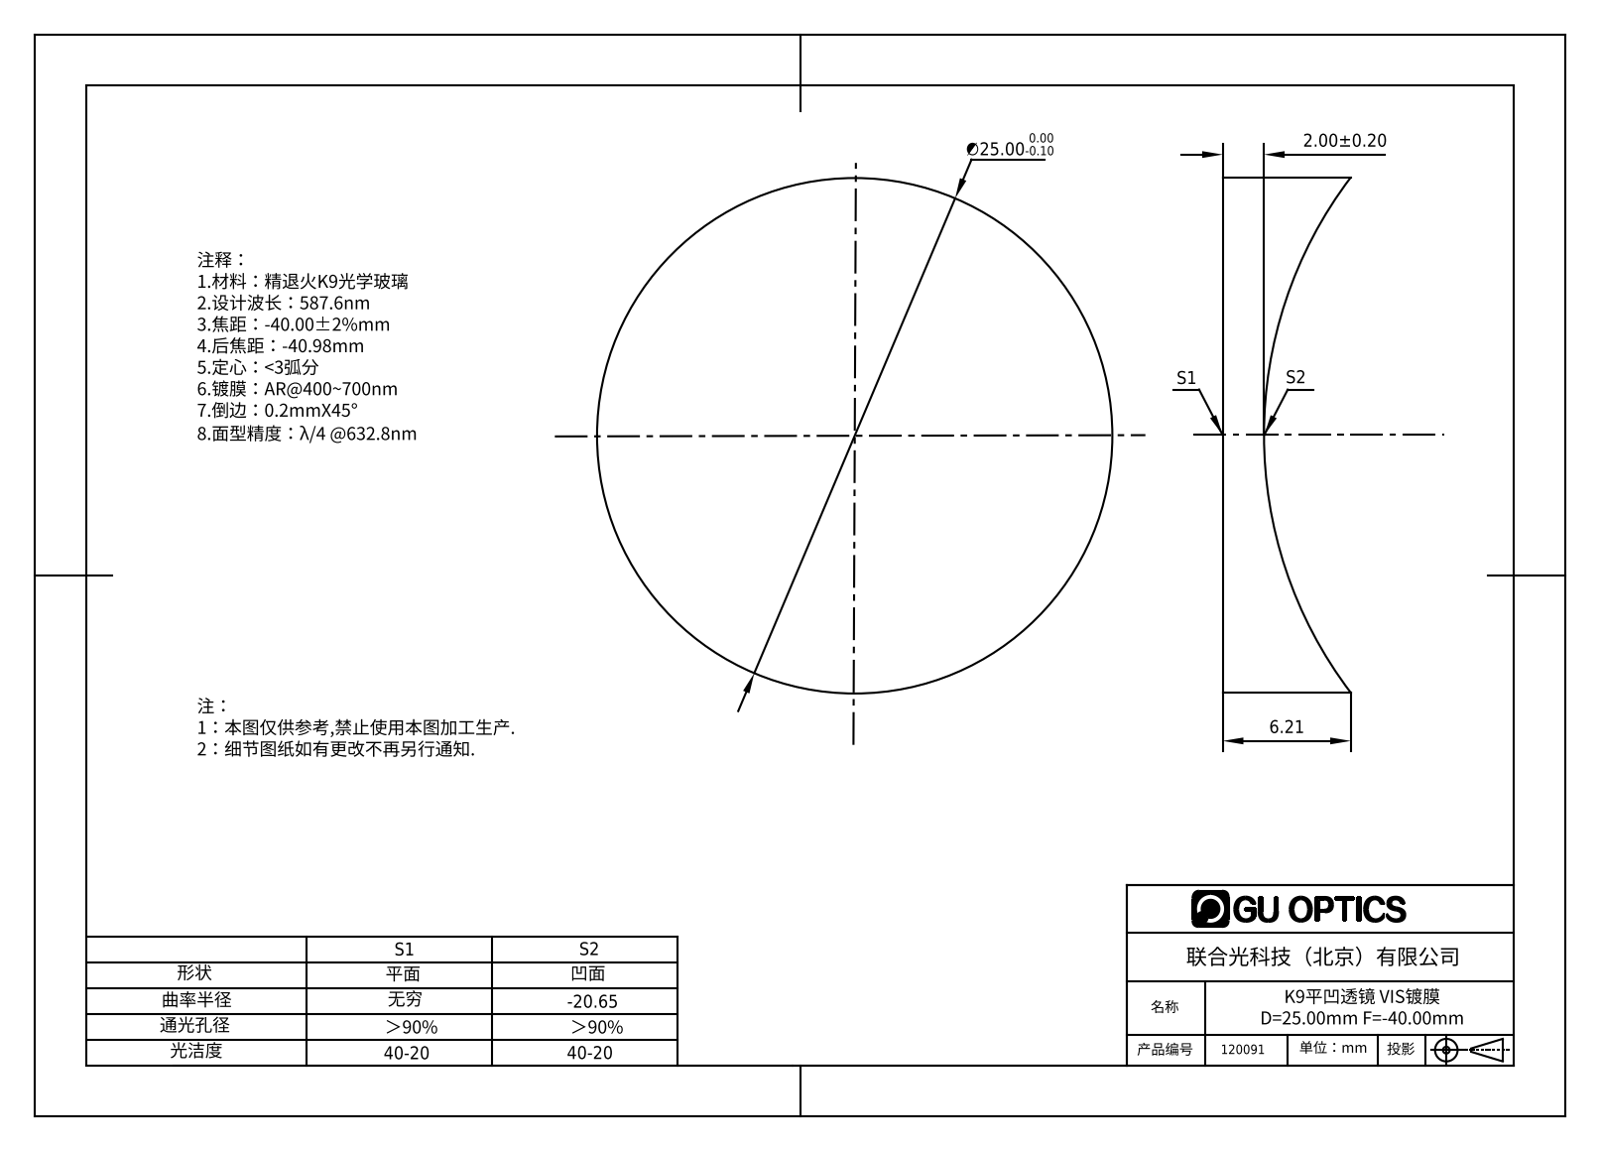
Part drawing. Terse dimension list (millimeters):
name: 120031
written by: SolidWorks 2016 (AUTOMOTIVE_DESIGN)
unit: mm
bodies: 1 solid, 5 faces (1 planar, 2 cylindrical, 2 other)
size: 25 × 25 × 6.21
volume: 1 977 mm³; area: 1 525 mm²
bosses: 1× ⌀25
